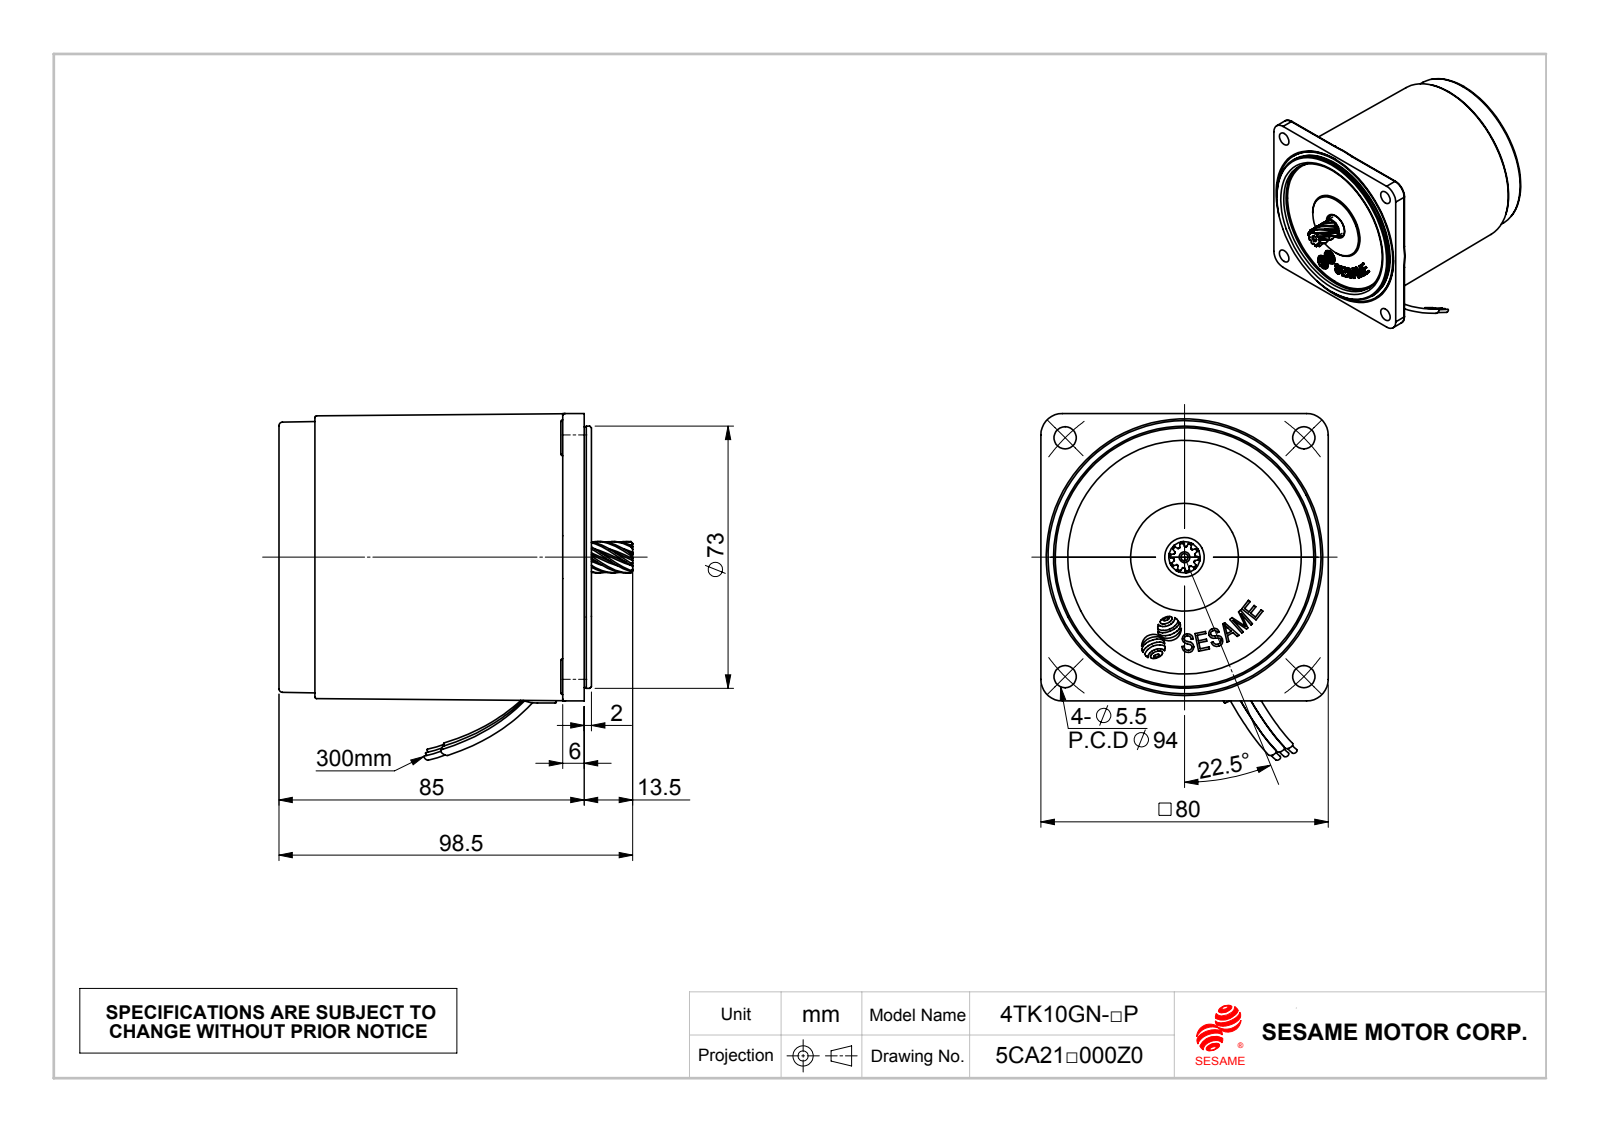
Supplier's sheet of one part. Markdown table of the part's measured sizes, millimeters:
| quantity | value |
| --- | --- |
| part name | 25GN_Default; 線扣; M425A_成品; C475-C473_C475成品-車工 |
| STEP written by | SolidWorks 2010 (CONFIG_CONTROL_DESIGN) |
| units | millimeters |
| bodies | 7 solids, 507 faces (145 planar, 202 cylindrical, 160 other) |
| overall size | 98.5 × 96.51 × 80 |
| volume | 420 184 mm³ |
| surface area | 49 972 mm² |
| round holes (diameter × count) | 6.2 × 4, 2 × 1, 7.2 × 1, 9.5 × 1, 11 × 1, 60 × 1, 65 × 1, 75.4 × 1 |
| round bosses / shafts (diameter × count) | 76 × 1, 75.05 × 1, 72.93 × 1, 72.53 × 1, 10 × 1, 9.4 × 1, 9.3 × 1, 8.75 × 1 |
| partial cylindrical surfaces (radius × count) | 0.25 × 8, 0.61 × 8, 1.16 × 8, 1.29 × 8, 2.26 × 8, 0.16 × 4, 0.45 × 4, 0.5 × 4 |
| main face-to-face distances | 1, 0.5, 84, 82.4, 82.5, 0.6, 83, 1.6, 1.5, 83.5 |
| hole center spacings | 46.99, 66.46, 93.99 |
